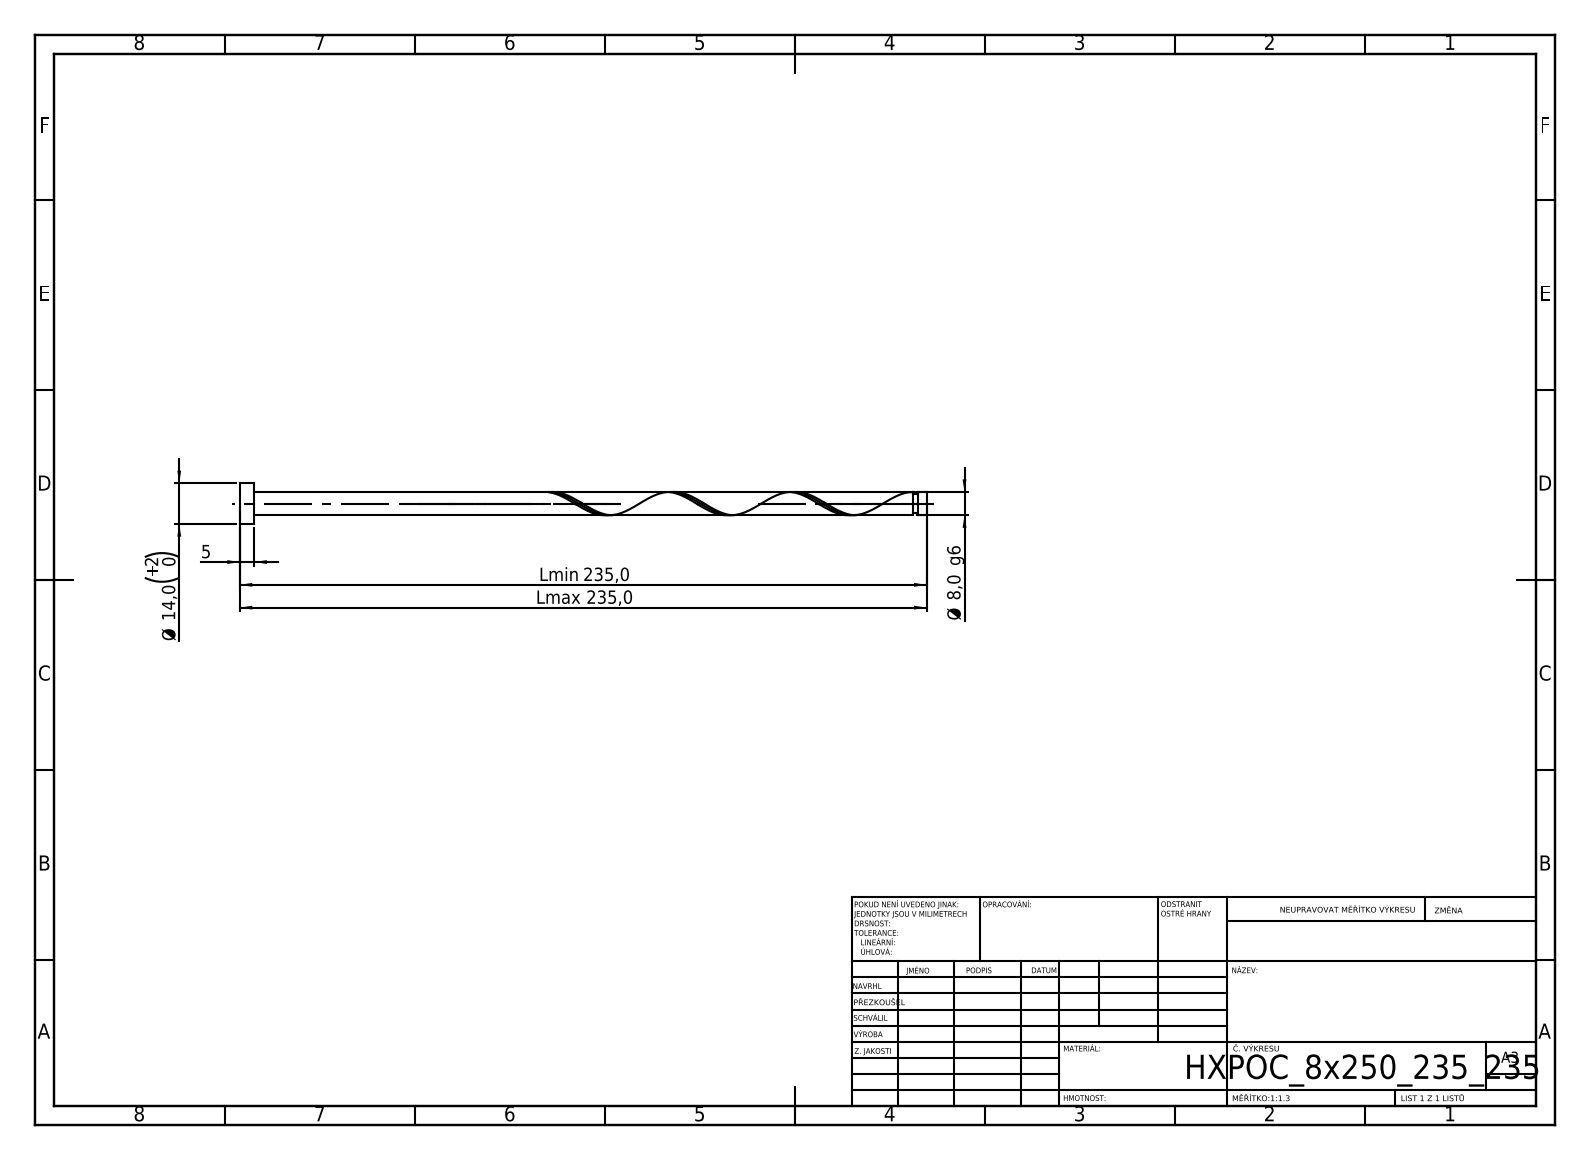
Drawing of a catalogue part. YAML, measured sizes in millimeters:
step_written_by: "SolidWorks 2019 (CONFIG_CONTROL_DESIGN)"
units: millimeters
bodies: {solids: 1, faces: 21, planar: 6, cylindrical: 14, other: 1}
overall_size: [235, 14, 14]
volume: 12182
surface_area: 6454
round_bosses_or_shafts:
  - {diameter: 14, count: 1}
  - {diameter: 8, count: 1}
  - {diameter: 6.4, count: 1}
face_to_face_distances: [5, 235, 230, 232.12, 227.12, 2.88, 230.52, 225.52, 1.6, 4.48]
